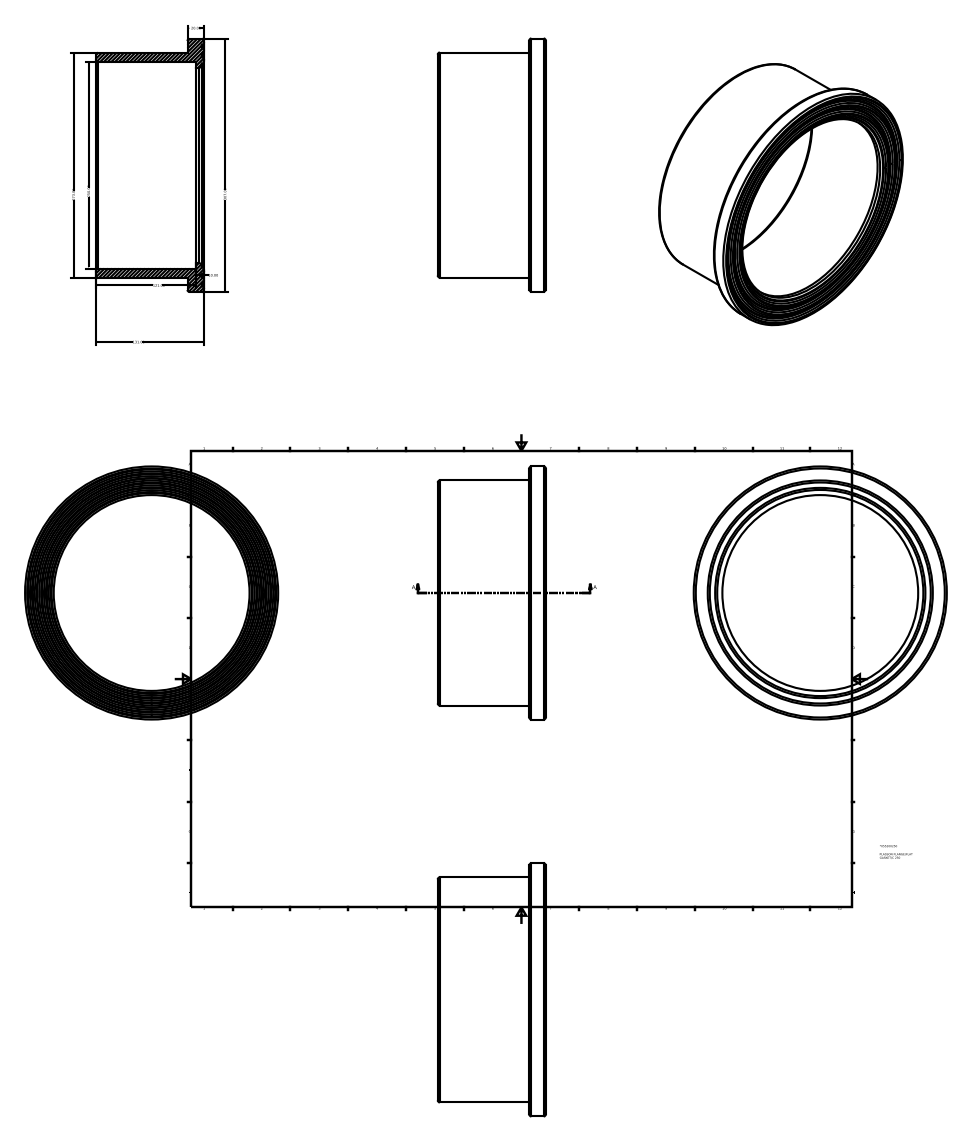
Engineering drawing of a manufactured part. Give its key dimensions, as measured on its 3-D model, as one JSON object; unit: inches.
{"part_name": "(_AS)055200250", "step_written_by": "Autodesk Inventor 2015 (AUTOMOTIVE_DESIGN)", "units": "inches", "bodies": {"solids": 1, "faces": 28, "planar": 9, "cylindrical": 4, "other": 15}, "overall_size": [12.087, 12.087, 5.157], "volume_in3": 94.28, "surface_area_in2": 425.8, "round_holes": [[9.35, 1], [9.843, 1]], "round_bosses_or_shafts": [[12.087, 1], [10.748, 1]], "face_to_face_distances": [0.394, 4.37, 4.764, 5.039, 0.669, 0.276, 5.157, 0.787, 0.118]}
